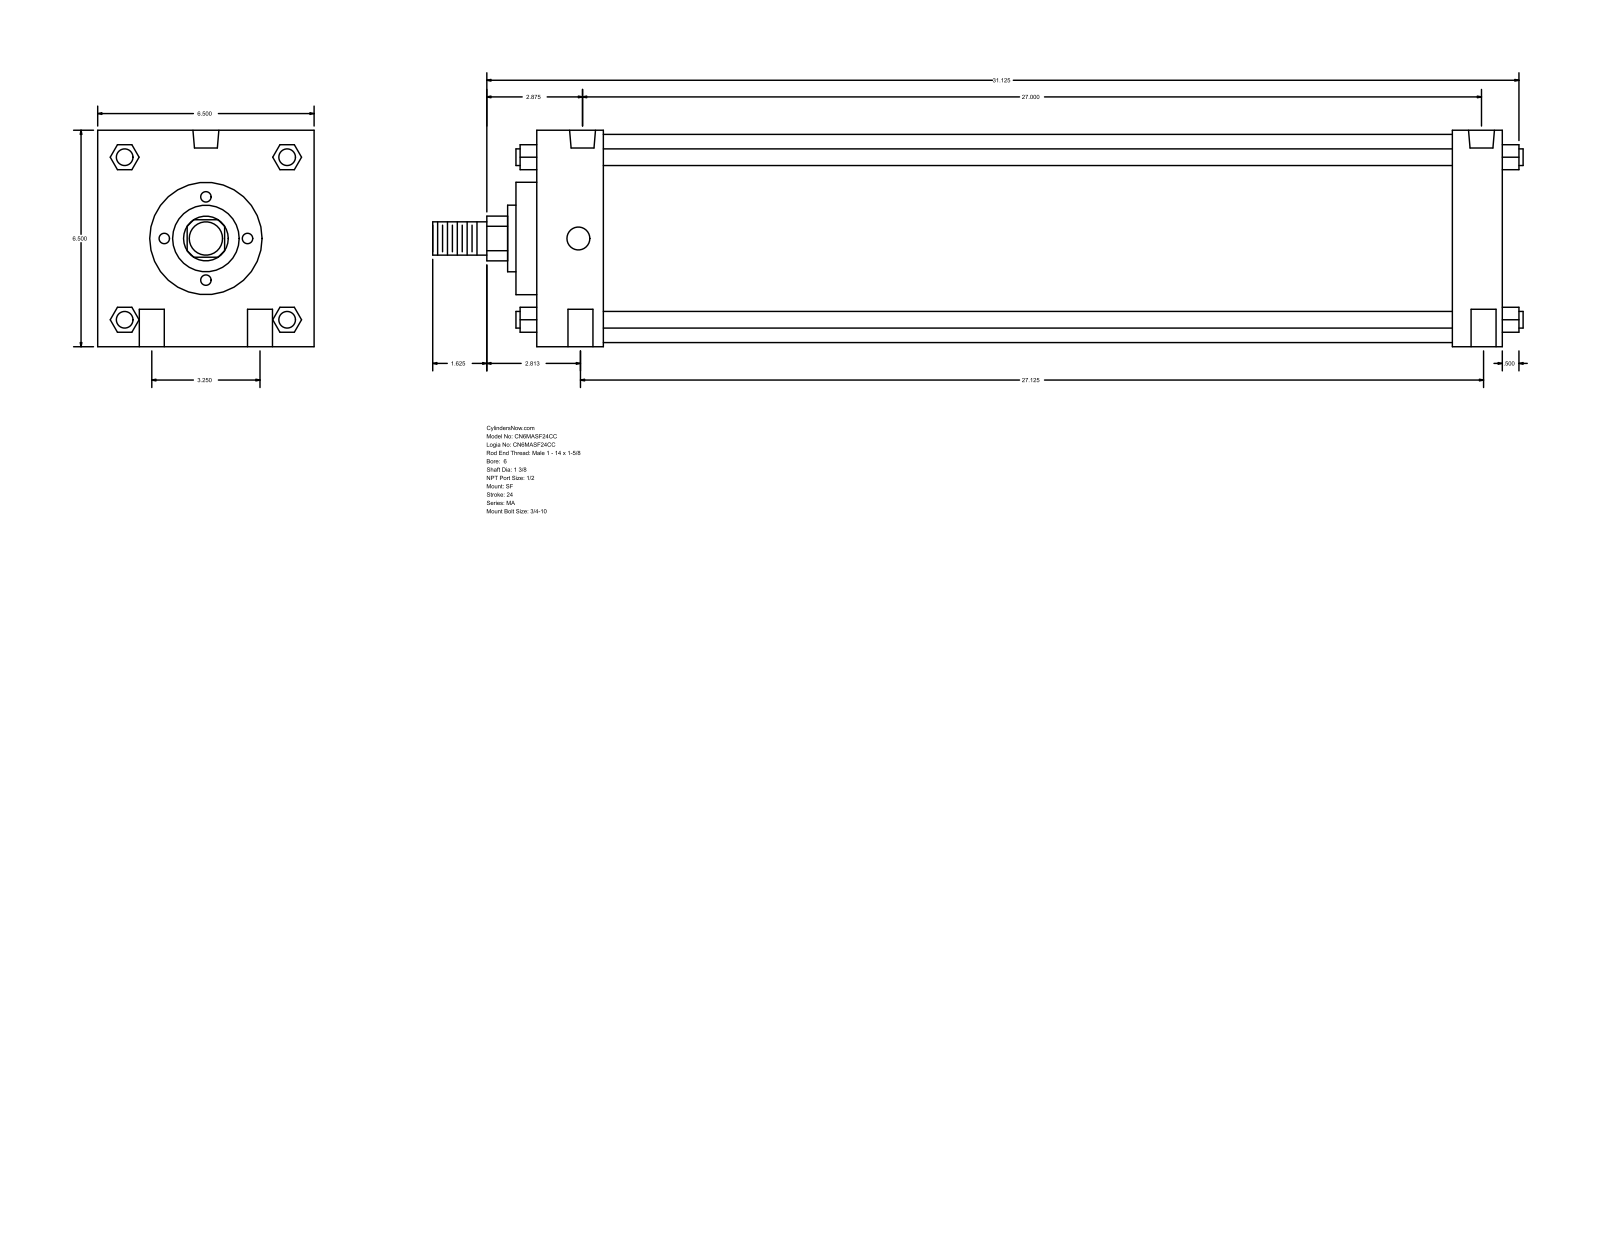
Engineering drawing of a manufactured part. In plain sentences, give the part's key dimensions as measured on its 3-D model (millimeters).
The part is named "MA_SF__0600_1.375". Its 3-D file was written by "GSSL Pune (CONFIG_CONTROL_DESIGN)". It is 0 solids with 126 faces: 95 planar, 31 cylindrical and 0 other. Overall it measures 831.85 by 165.1 by 165.1 millimeters. Round holes: 4 of diameter 19.05, 2 of diameter 17.46, 2 of diameter 19.77. Round bosses or shafts: 4 of diameter 12.7, 1 of diameter 158.75, 1 of diameter 85.72, 1 of diameter 50.8, 1 of diameter 34.92, 1 of diameter 25.4. Partial cylindrical surfaces (rounded edges, fillets, slot ends): 1 of radius 17.06. The main face-to-face distances are 165.1, 736.6, 698.5, 50.8, 38.1, 647.7, 685.8, 66.67, 15.87, 714.37. The hole center spacings are 41.3, 82.54, 685.8, 688.62, 688.63, 688.97, 693.9.
